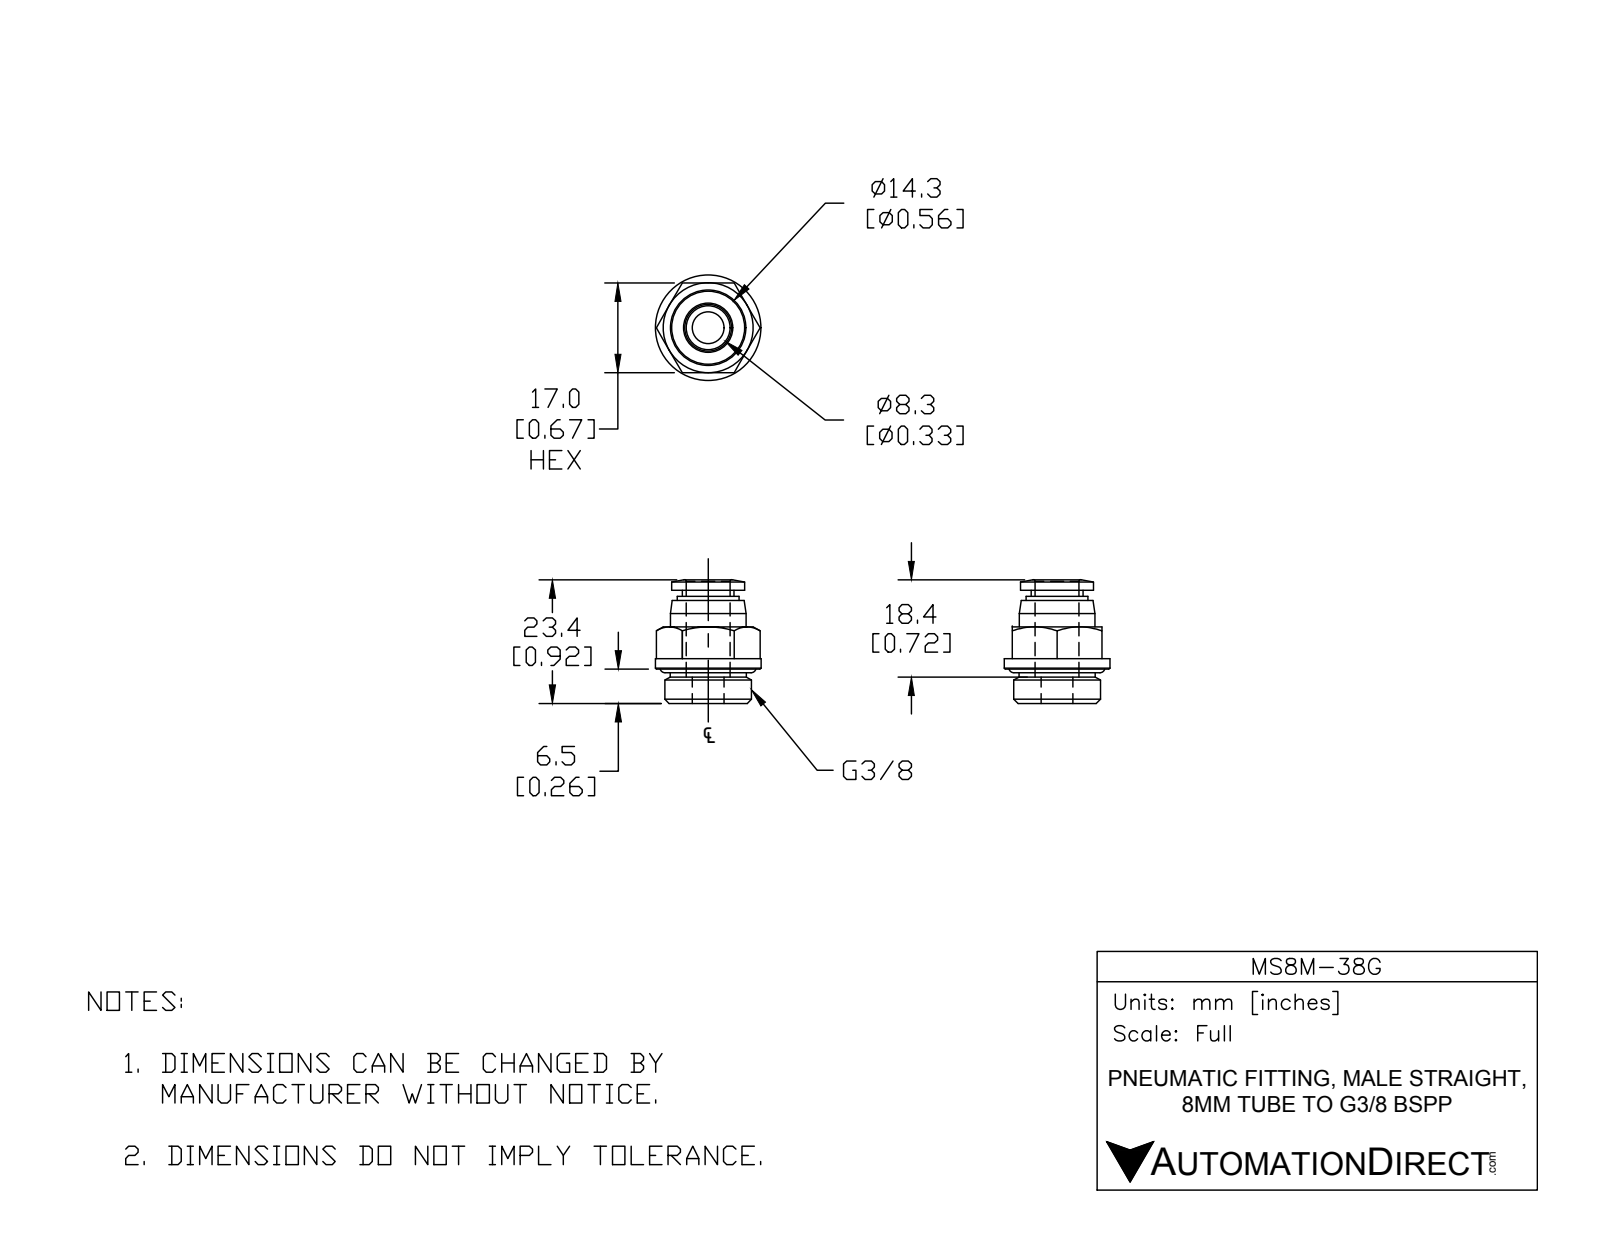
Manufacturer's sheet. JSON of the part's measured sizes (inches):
{"part_name": "MS8M-38G", "step_written_by": "SolidWorks 2018 (AUTOMOTIVE_DESIGN)", "units": "inches", "bodies": {"solids": 2, "faces": 59, "planar": 16, "cylindrical": 18, "other": 25}, "overall_size": [0.921, 0.787, 0.787], "volume_in3": 0.216, "surface_area_in2": 4.405, "round_holes": [[0.236, 1], [0.327, 1]], "round_bosses_or_shafts": [[0.787, 1], [0.646, 1], [0.567, 1], [0.563, 1], [0.543, 1], [0.461, 1], [0.386, 1]], "face_to_face_distances": [0.669, 0.571, 0.843, 0.272, 0.335, 0.236, 0.508, 0.197, 0.768, 0.433]}
